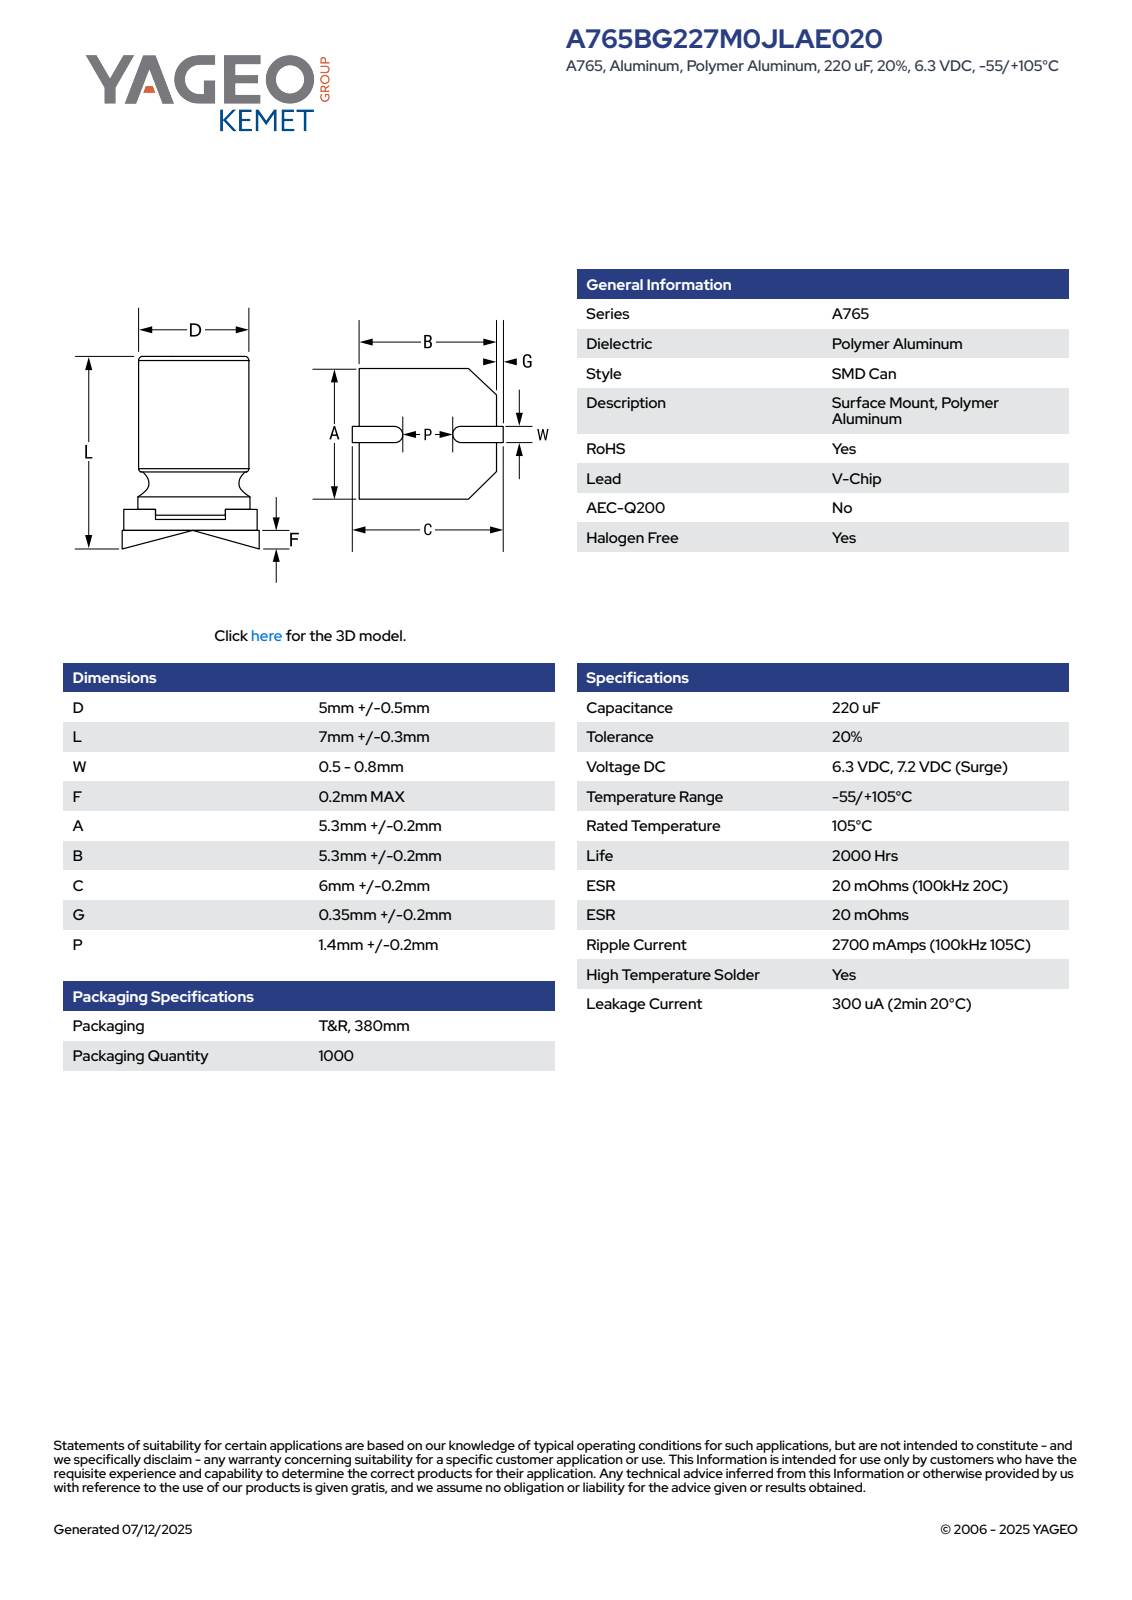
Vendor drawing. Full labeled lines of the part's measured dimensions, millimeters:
Part name (STEP PRODUCT): CAC_KS_5X7_D5.5L7.3W0.8F0.2A5.5B5.5C6.2P1.6
STEP written by: SolidWorks 2021 (AUTOMOTIVE_DESIGN)
Units: millimetres
Bodies: 5 solids, 76 faces (59 planar, 11 cylindrical, 6 other)
Overall size (bounding box): 7.3 × 6.2 × 5.5
Volume: 160 mm³ · Surface area: 251 mm²
Round bosses / shafts (diameter × count): ⌀5.26 ×1
Partial cylindrical surfaces — rounded edges, fillets, slot ends (radius × count): R0.2 ×2, R2.18 ×1, R2.75 ×1
Main face-to-face distances: 0.37, 7.1, 6.73, 5.5, 0.57, 7.3, 1.5, 4, 1.82, 2.02
